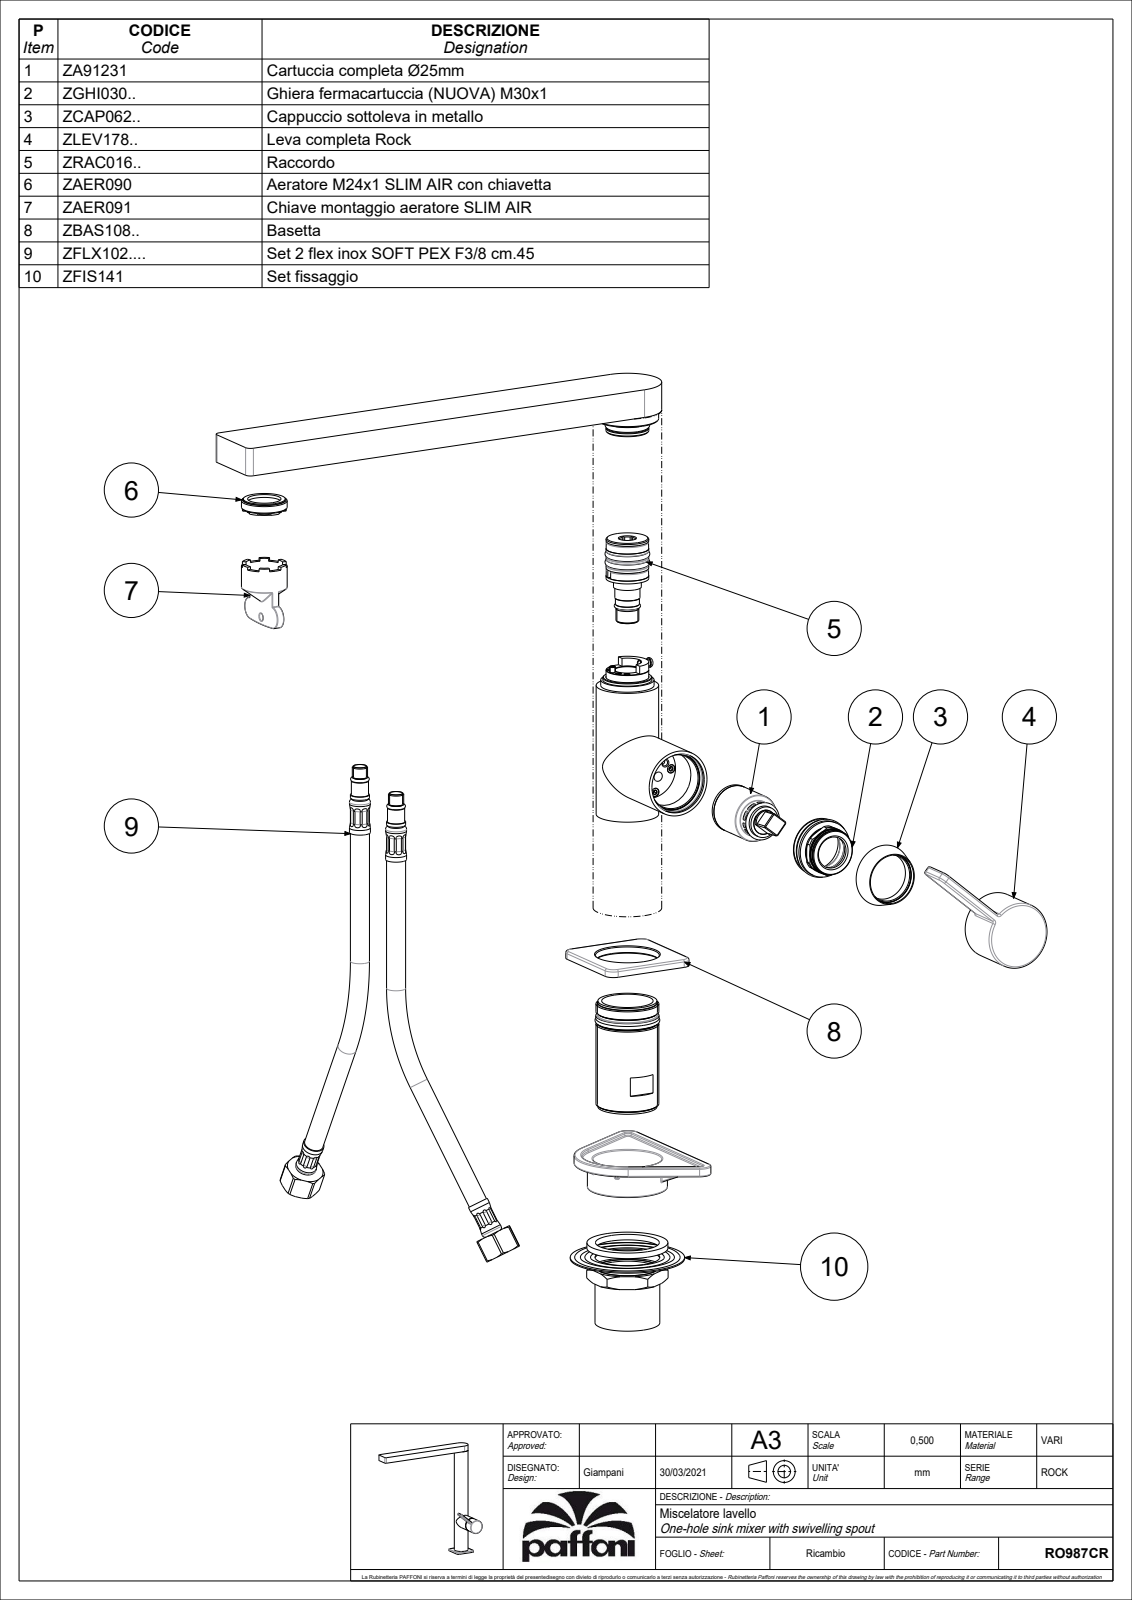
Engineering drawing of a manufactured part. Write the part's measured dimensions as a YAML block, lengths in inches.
part_name: "RO987CR"
step_written_by: "CREO PARAMETRIC BY PTC INC, 2020044 (CONFIG_CONTROL_DESIGN)"
units: inches
bodies: {solids: 2, faces: 210, planar: 74, cylindrical: 87, other: 49}
overall_size: [11.417, 10.433, 4.16]
volume: 27.18
surface_area: 130.2
round_holes:
  - {diameter: 0.118, count: 1}
  - {diameter: 0.165, count: 1}
  - {diameter: 0.976, count: 1}
  - {diameter: 1.031, count: 1}
  - {diameter: 1.063, count: 1}
  - {diameter: 1.102, count: 1}
  - {diameter: 1.142, count: 1}
  - {diameter: 1.205, count: 1}
  - {diameter: 1.248, count: 1}
  - {diameter: 1.319, count: 1}
  - {diameter: 1.752, count: 1}
round_bosses_or_shafts:
  - {diameter: 1.378, count: 2}
  - {diameter: 1.535, count: 1}
  - {diameter: 1.417, count: 1}
  - {diameter: 1.339, count: 1}
  - {diameter: 1.307, count: 1}
  - {diameter: 1.299, count: 1}
  - {diameter: 1.181, count: 1}
  - {diameter: 0.728, count: 1}
partial_cylinders:
  - {radius: 0.039, count: 12}
  - {radius: 0.118, count: 8}
  - {radius: 0.197, count: 4}
  - {radius: 0.059, count: 2}
  - {radius: 0.138, count: 1}
face_to_face_distances: [0.591, 1.417, 10.827, 11.417, 0.157, 10.669, 11.26, 3.885, 2.467, 0.177]
